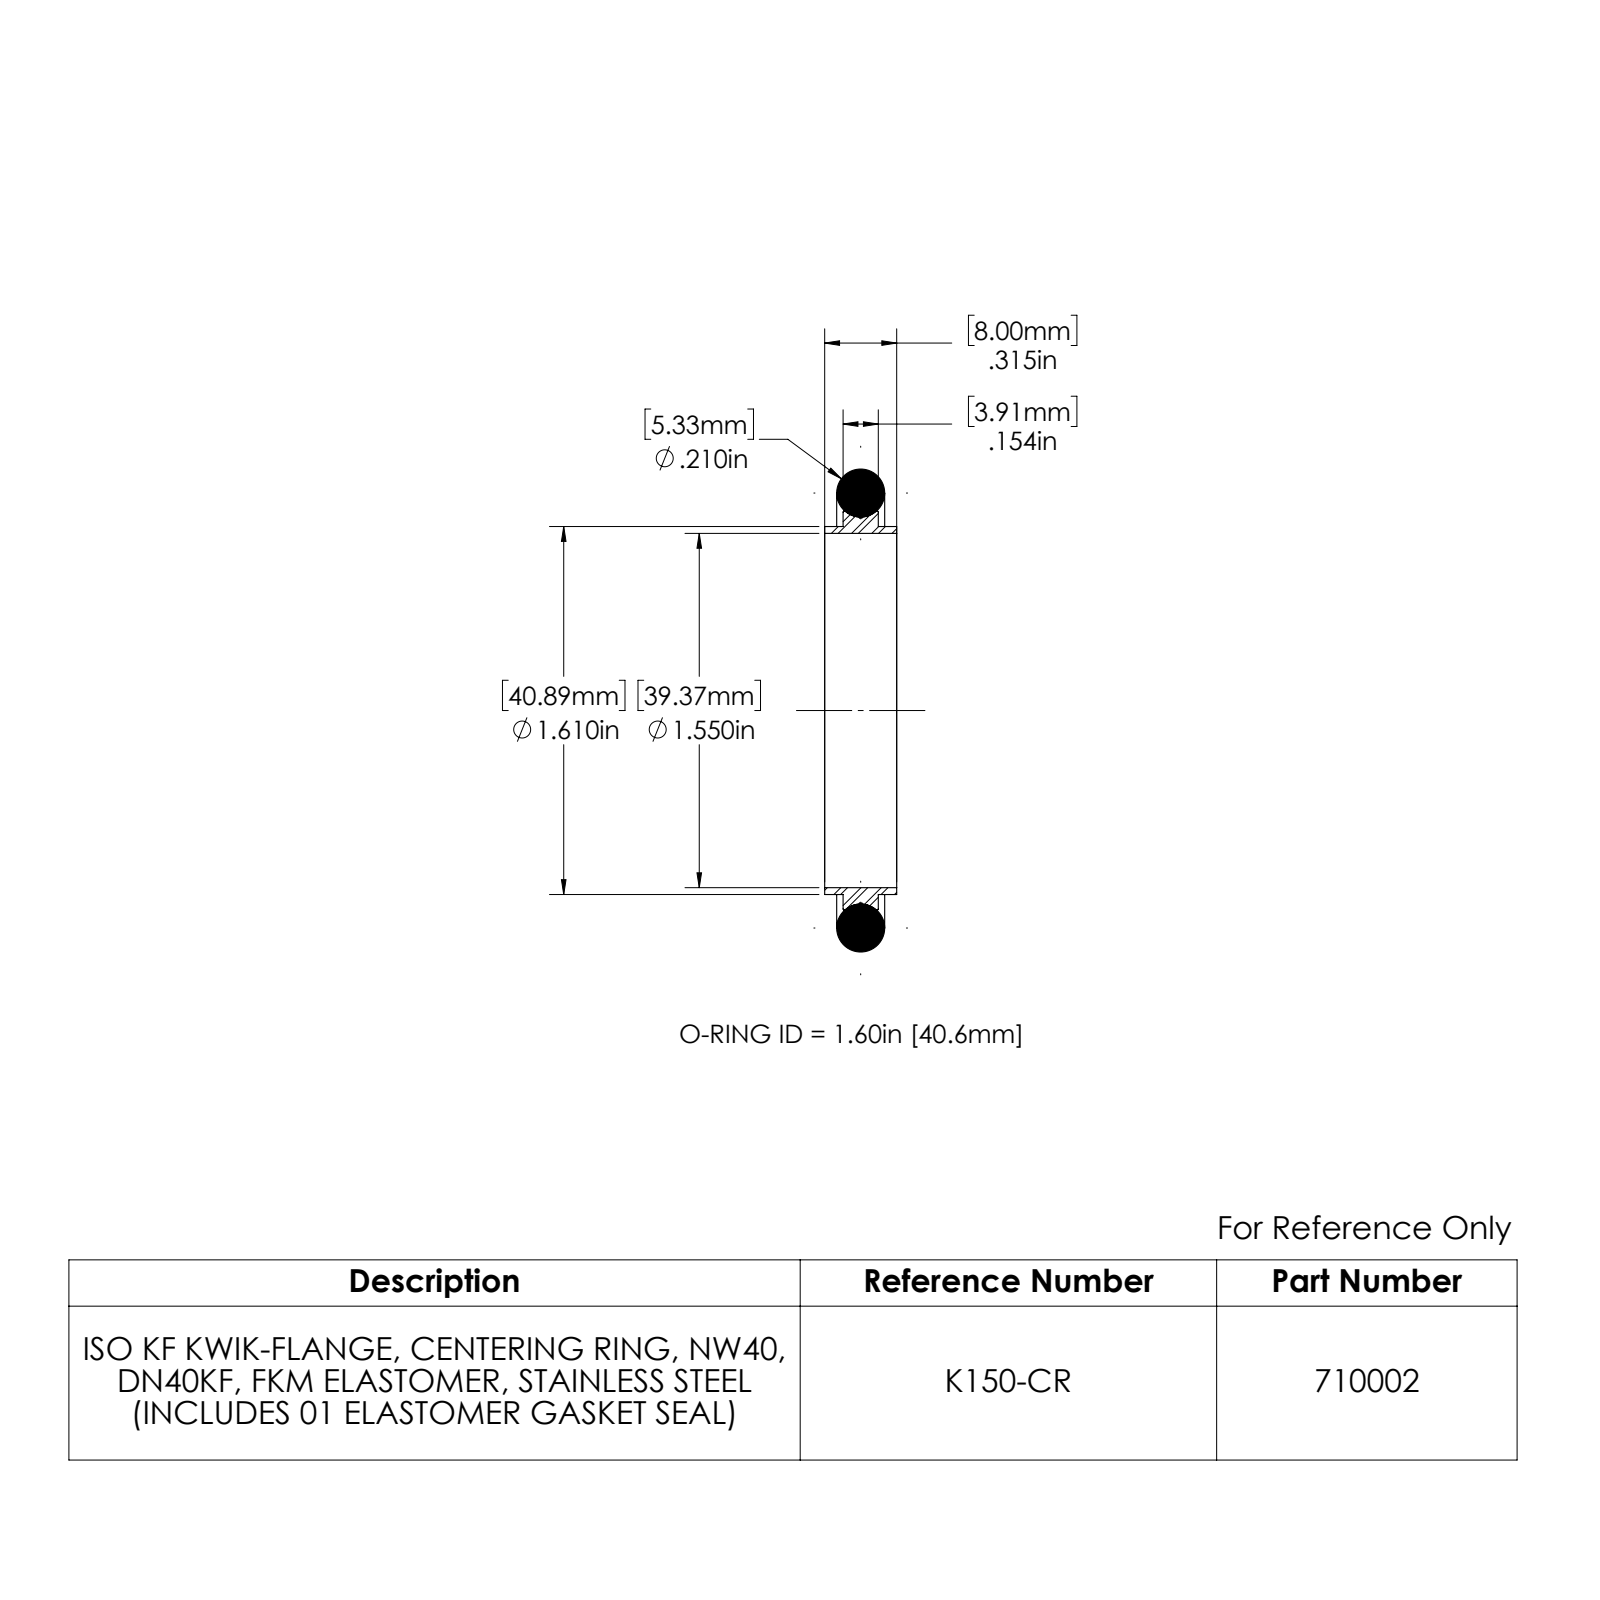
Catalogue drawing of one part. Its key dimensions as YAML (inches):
part_name: "710002"
step_written_by: "SolidWorks 2022 (AUTOMOTIVE_DESIGN)"
units: inches
bodies: {solids: 2, faces: 30, planar: 4, cylindrical: 10, other: 16}
overall_size: [2.099, 2.099, 0.315]
volume: 0.294
surface_area: 8.155
round_holes:
  - {diameter: 1.55, count: 1}
round_bosses_or_shafts:
  - {diameter: 1.746, count: 1}
  - {diameter: 1.61, count: 1}
face_to_face_distances: [0.154, 0.08, 0.235, 0.315]
